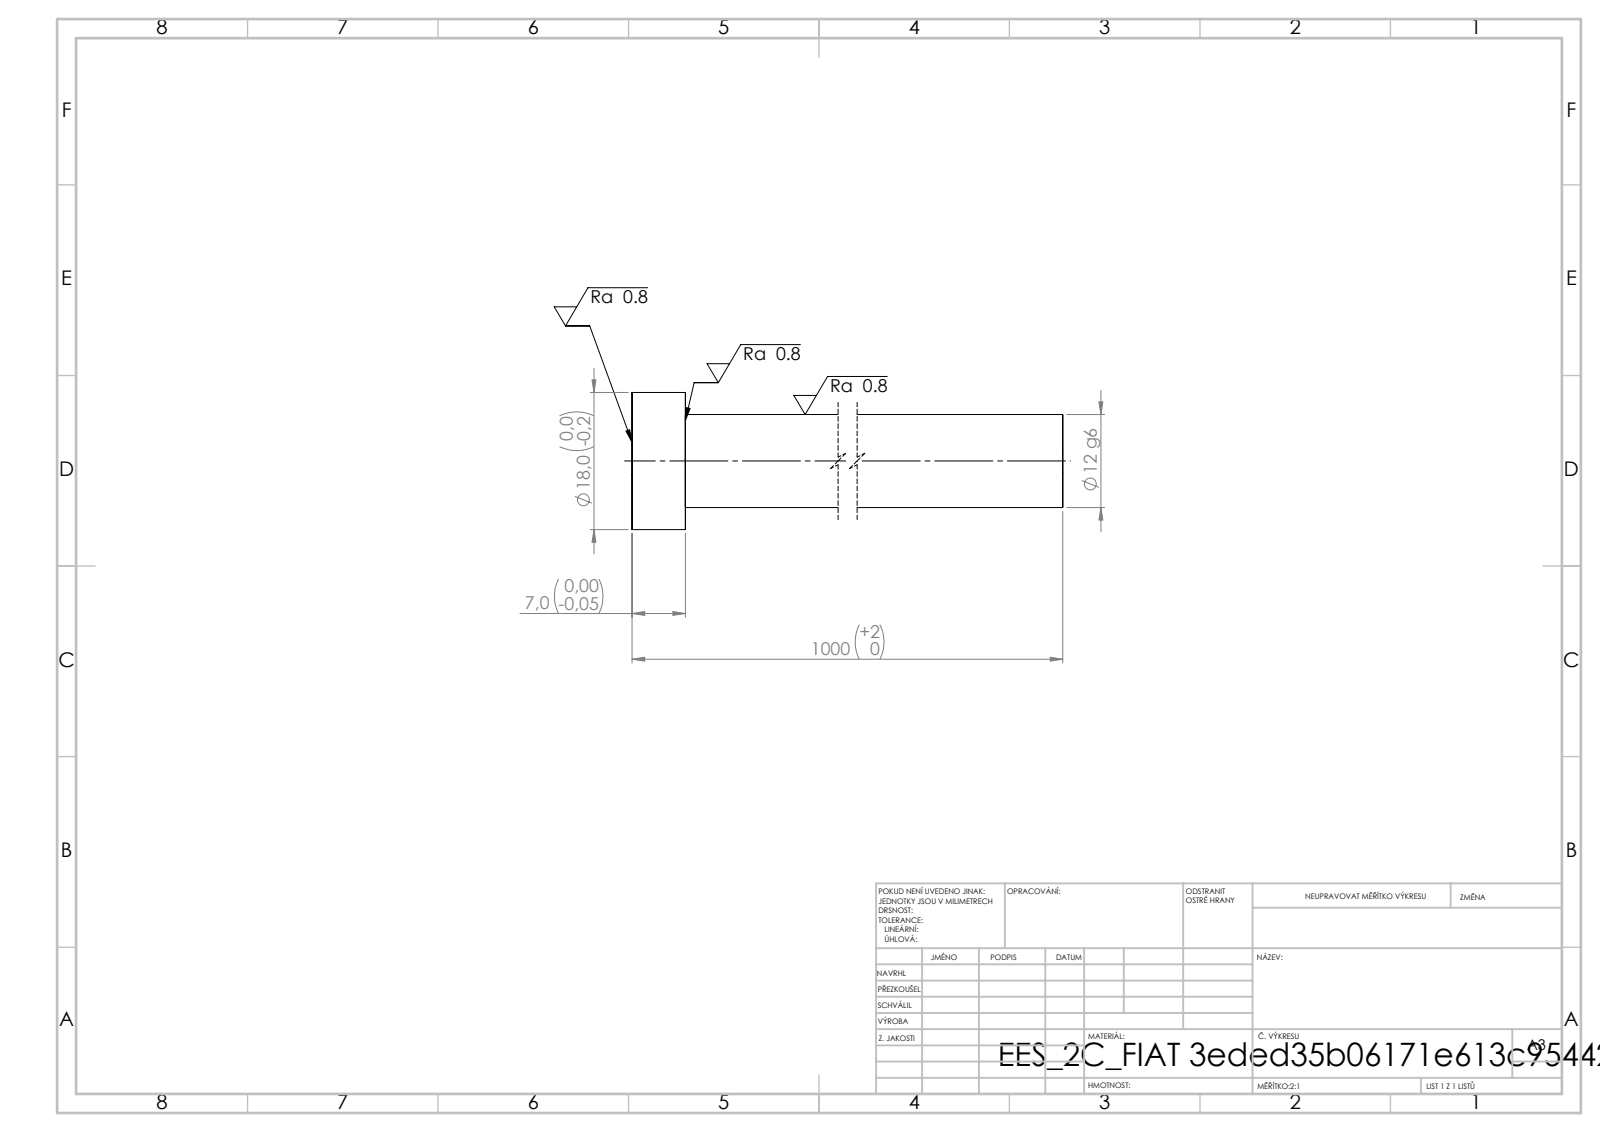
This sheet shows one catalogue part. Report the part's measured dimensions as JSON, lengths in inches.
{"step_written_by": "SolidWorks 2019 (CONFIG_CONTROL_DESIGN)", "units": "inches", "bodies": {"solids": 1, "faces": 7, "planar": 3, "cylindrical": 4, "other": 0}, "overall_size": [39.37, 0.709, 0.709], "volume_in3": 7.192, "surface_area_in2": 60.39, "round_bosses_or_shafts": [[0.709, 1], [0.48, 1]], "face_to_face_distances": [0.276, 39.37, 39.094]}
